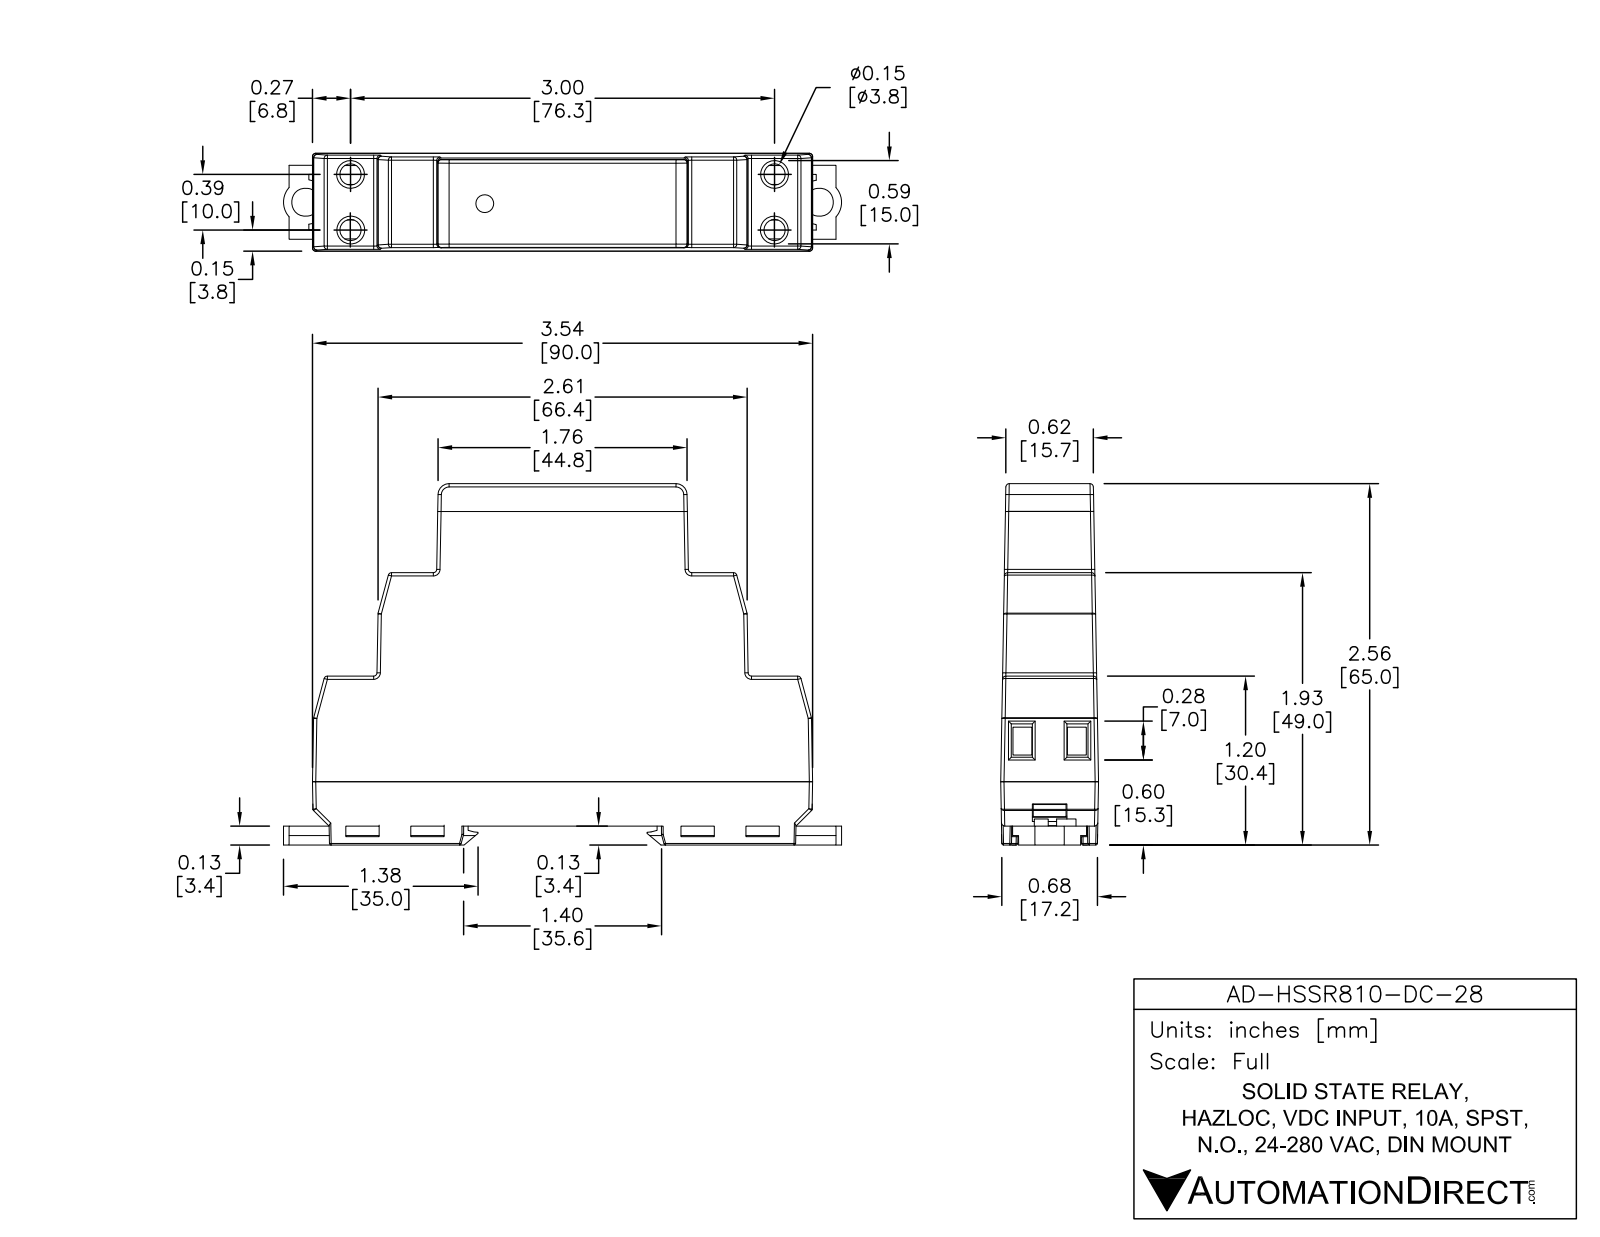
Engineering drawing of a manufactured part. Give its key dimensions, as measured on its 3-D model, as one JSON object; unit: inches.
{"part_name": "AD-HSSR810-DC-28", "step_written_by": "SolidWorks 2013 (AUTOMOTIVE_DESIGN)", "units": "inches", "bodies": {"solids": 35, "faces": 1270, "planar": 679, "cylindrical": 65, "other": 526}, "overall_size": [3.952, 2.619, 0.692], "volume_in3": 4.725, "surface_area_in2": 25.56, "round_holes": [[0.2, 4], [0.19, 2]], "round_bosses_or_shafts": [[0.175, 4], [0.1, 1]], "partial_cylinders_radius": [[0.02, 10], [0.024, 10], [0.012, 6], [0.079, 2], [0.15, 2], [45.93, 2]], "face_to_face_distances": [0.136, 2.559, 2.423, 0.134, 2.425, 1.929, 1.795, 1.793, 0.63, 1.197], "hole_center_spacings": [3.335, 0.379, 0.38, 0.4, 3.006, 3.033, 3.652]}
